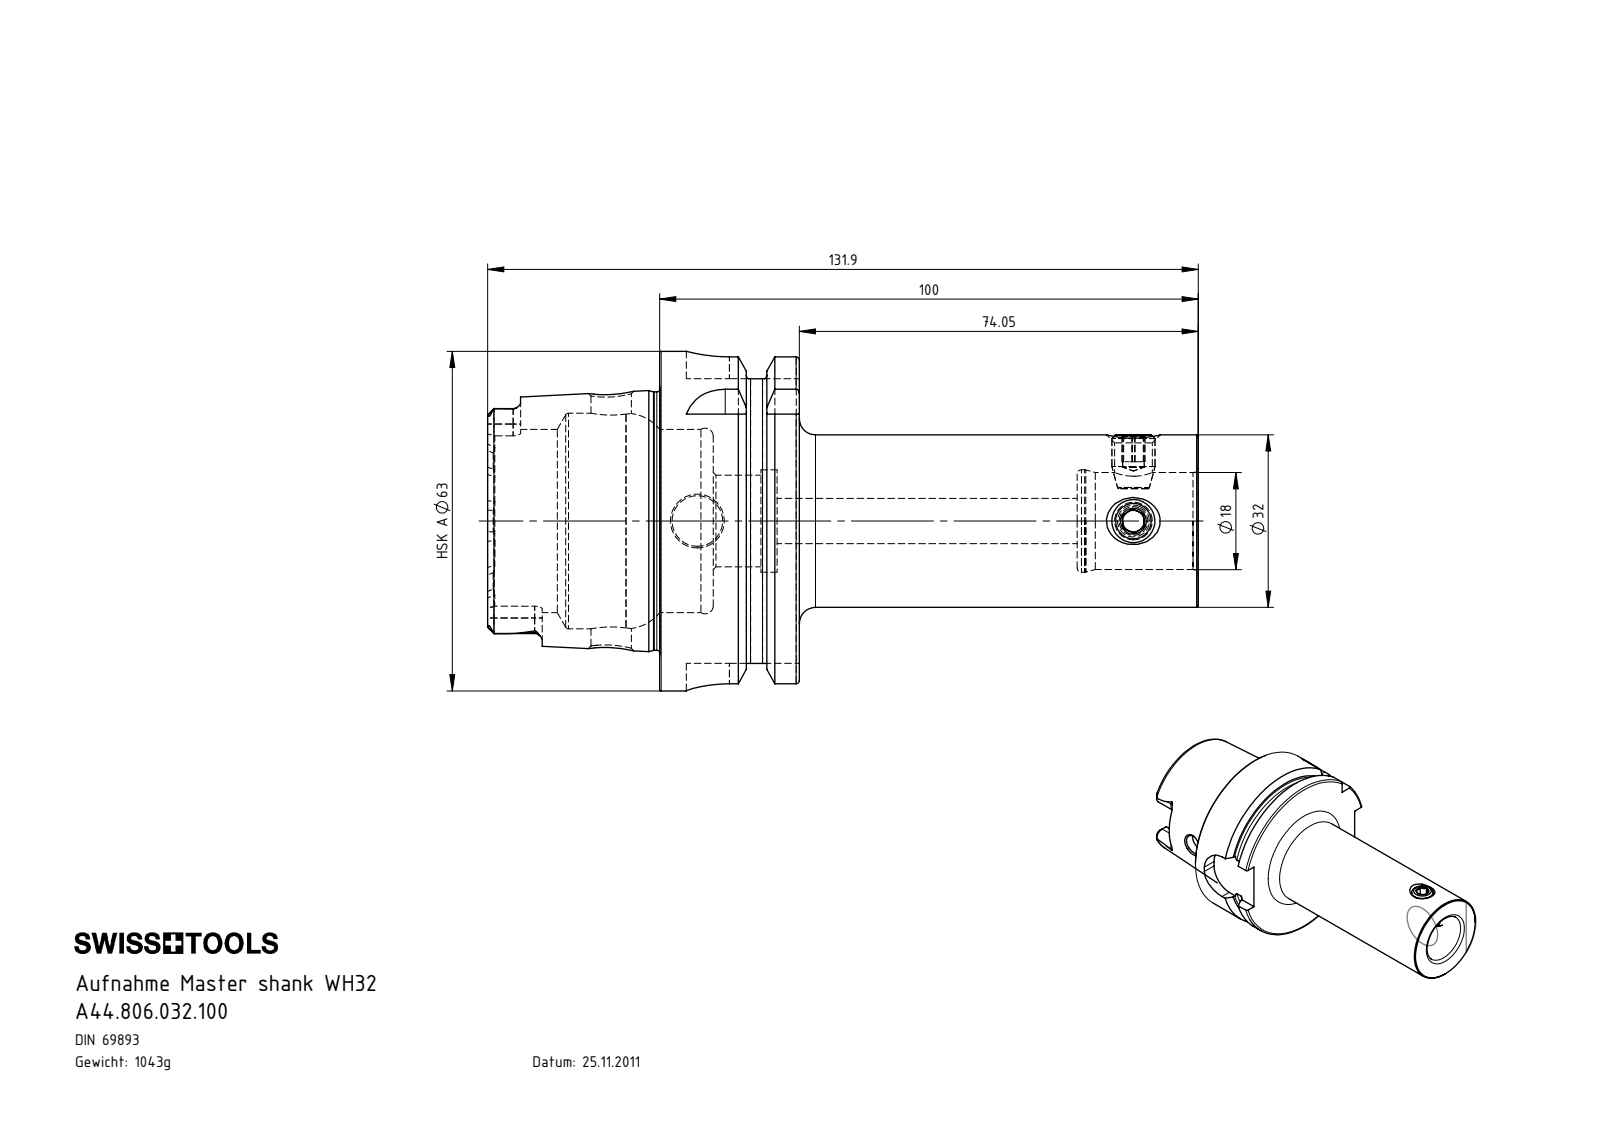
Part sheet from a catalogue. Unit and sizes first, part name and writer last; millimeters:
Units: millimetres
Overall size (bounding box): 131.9 × 63 × 63
Round holes (diameter × count): ⌀4 ×2, ⌀7 ×2, ⌀7.5 ×1, ⌀8.4 ×1, ⌀10 ×1, ⌀17 ×1, ⌀18 ×1, ⌀19 ×1, ⌀34 ×1, ⌀40 ×1
Round bosses / shafts (diameter × count): ⌀8 ×2, ⌀63 ×1, ⌀54.95 ×1, ⌀47.94 ×1, ⌀32 ×1
Partial cylindrical surfaces — rounded edges, fillets, slot ends (radius × count): R1.4 ×6, R2.88 ×4, R8 ×4
Main face-to-face distances: 25.95, 16, 9.95, 100, 90.05, 74.05, 31.9, 41.85, 57.85, 131.9
Hole centre spacings: 80.95, 96.95
Volume: 137 720 mm³ · Surface area: 33 435 mm²
Bodies: 4 solids, 271 faces (89 planar, 65 cylindrical, 117 other)
Part name (STEP PRODUCT): HA6-WH3.K01.100_C; A44.806.032.100; WH3-ER1.001.010
STEP written by: SolidWorks 2017 (CONFIG_CONTROL_DESIGN)
